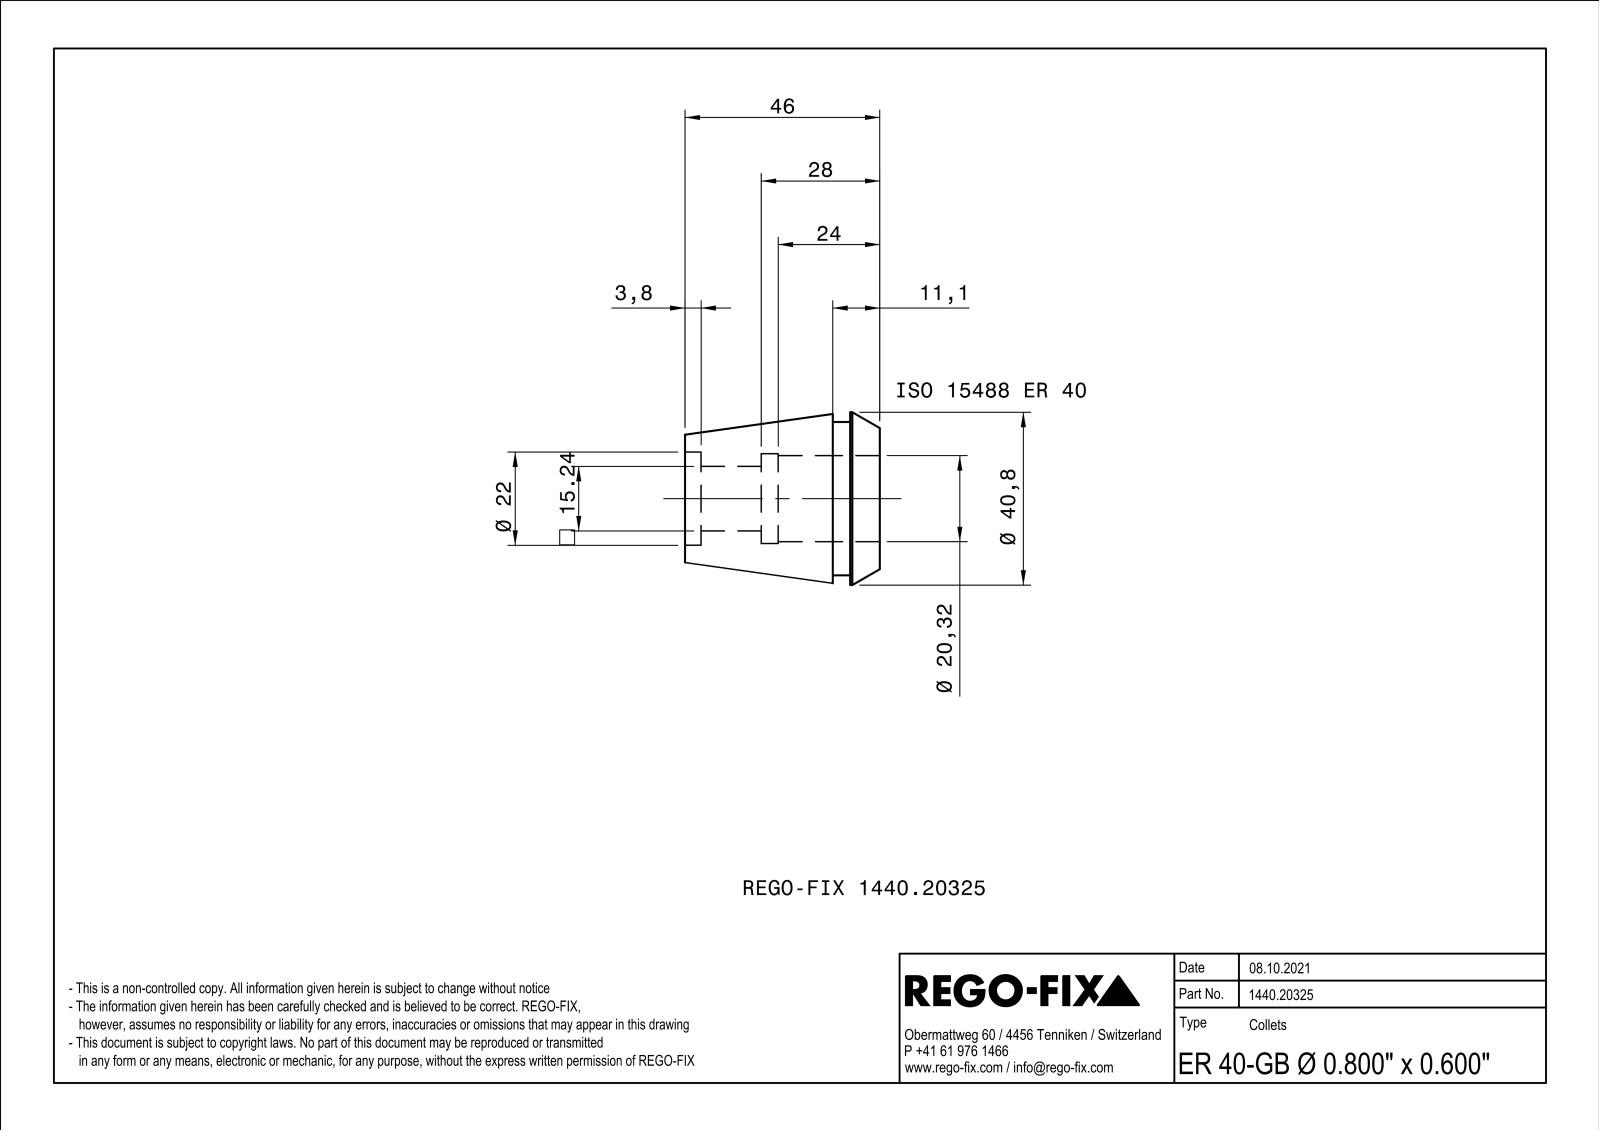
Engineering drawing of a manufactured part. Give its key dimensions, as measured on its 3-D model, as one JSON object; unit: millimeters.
{"part_name": "NOCUT", "step_written_by": "SIEMENS PLM Software Solid Edge ST10 (AUTOMOTIVE_DESIGN)", "units": "millimeters", "bodies": {"solids": 1, "faces": 168, "planar": 60, "cylindrical": 44, "other": 64}, "overall_size": [46, 40.79, 40.79], "volume_mm3": 28691, "surface_area_mm2": 13949, "round_holes": [[20.32, 1], [21.2, 1], [21.6, 1], [22, 1]], "round_bosses_or_shafts": [[36.2, 1]], "partial_cylinders_radius": [[9.2, 1], [10.5, 1]], "face_to_face_distances": [1, 46, 7.4, 8.4, 7, 39, 11.1, 4.1, 34.9, 15.8]}
